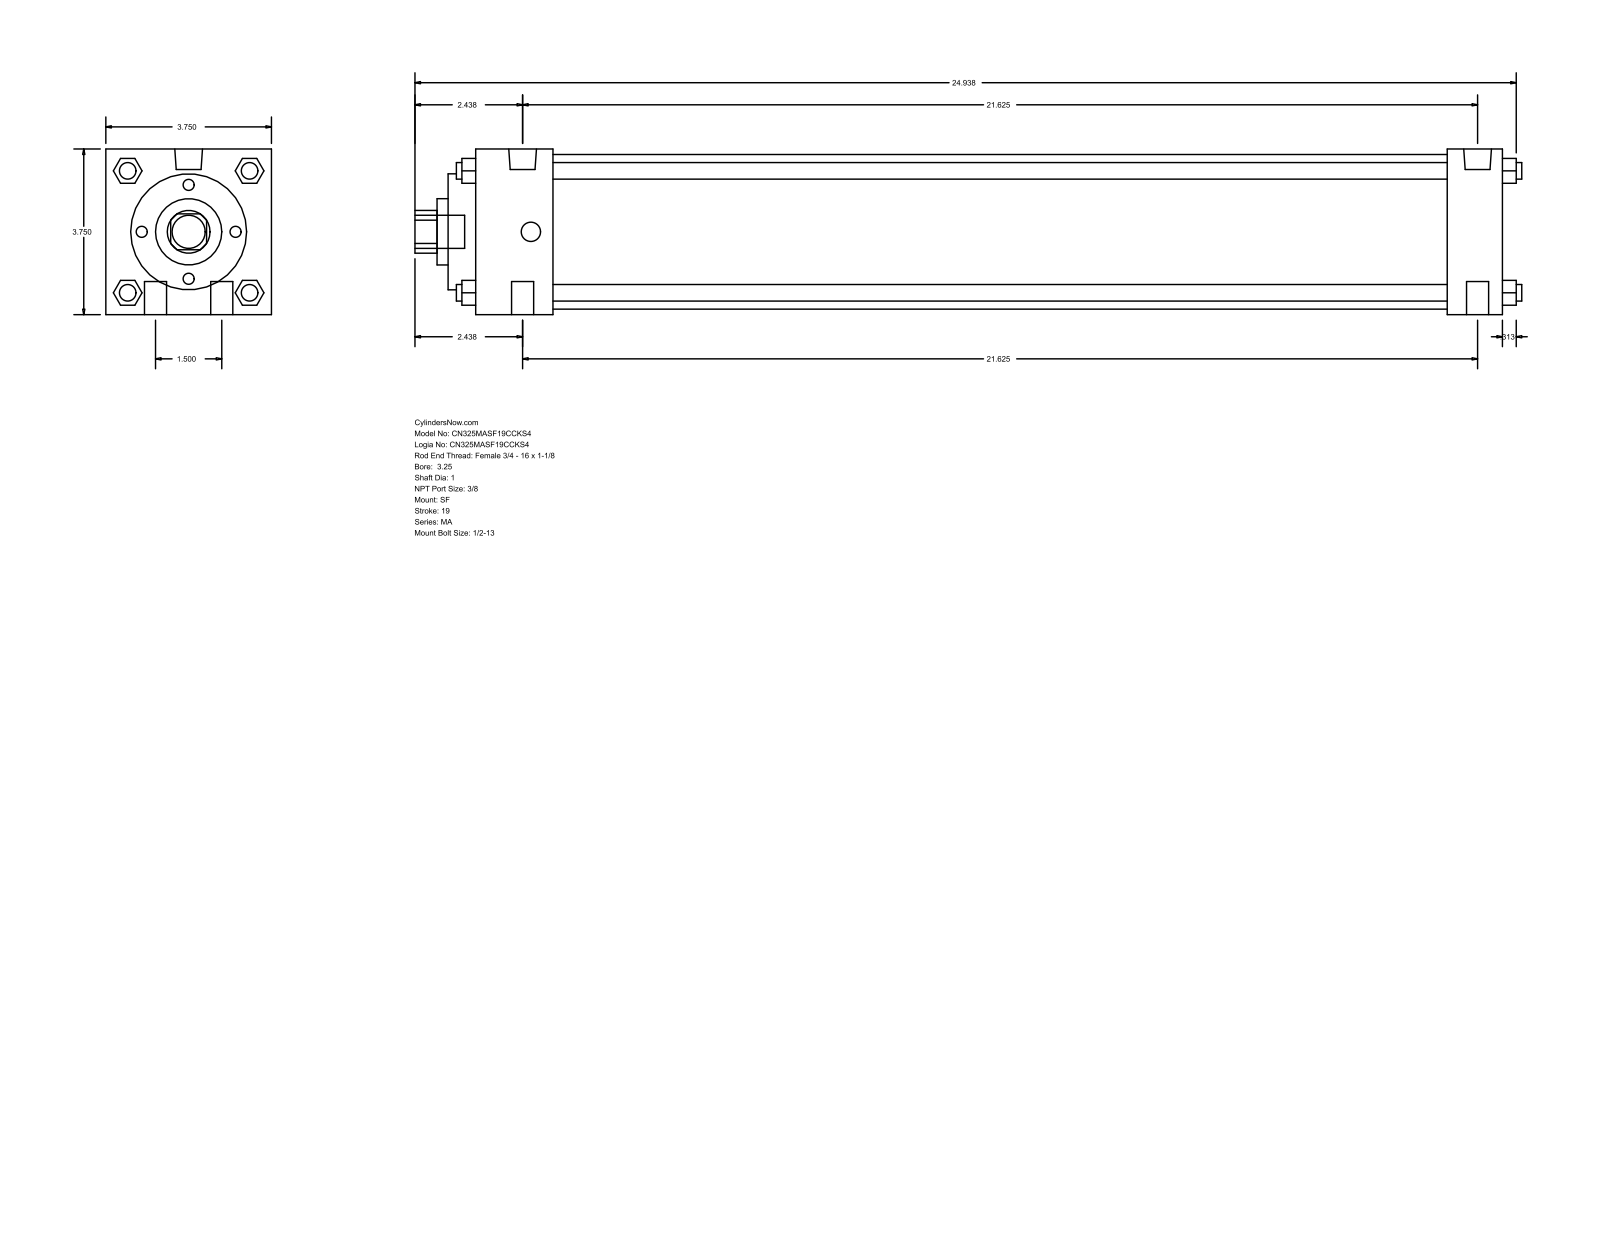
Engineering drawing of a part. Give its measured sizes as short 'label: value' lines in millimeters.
name: MA_SF__0325_1
written by: GSSL Pune (CONFIG_CONTROL_DESIGN)
unit: mm
bodies: 0 solids, 126 faces (95 planar, 31 cylindrical, 0 other)
size: 636.59 × 95.25 × 95.25
holes: 1× ⌀25.4, 1× ⌀38.1, 1× ⌀66.67, 1× ⌀88.9
bosses: 4× ⌀12.7, 4× ⌀9.53, 2× ⌀15.93, 2× ⌀11.11, 1× ⌀19.05
rounds: 1× R12.29
face distances: 95.24, 590.56, 15.87, 558.81, 31.75, 44.46, 514.35, 546.1, 60.33, 574.68
